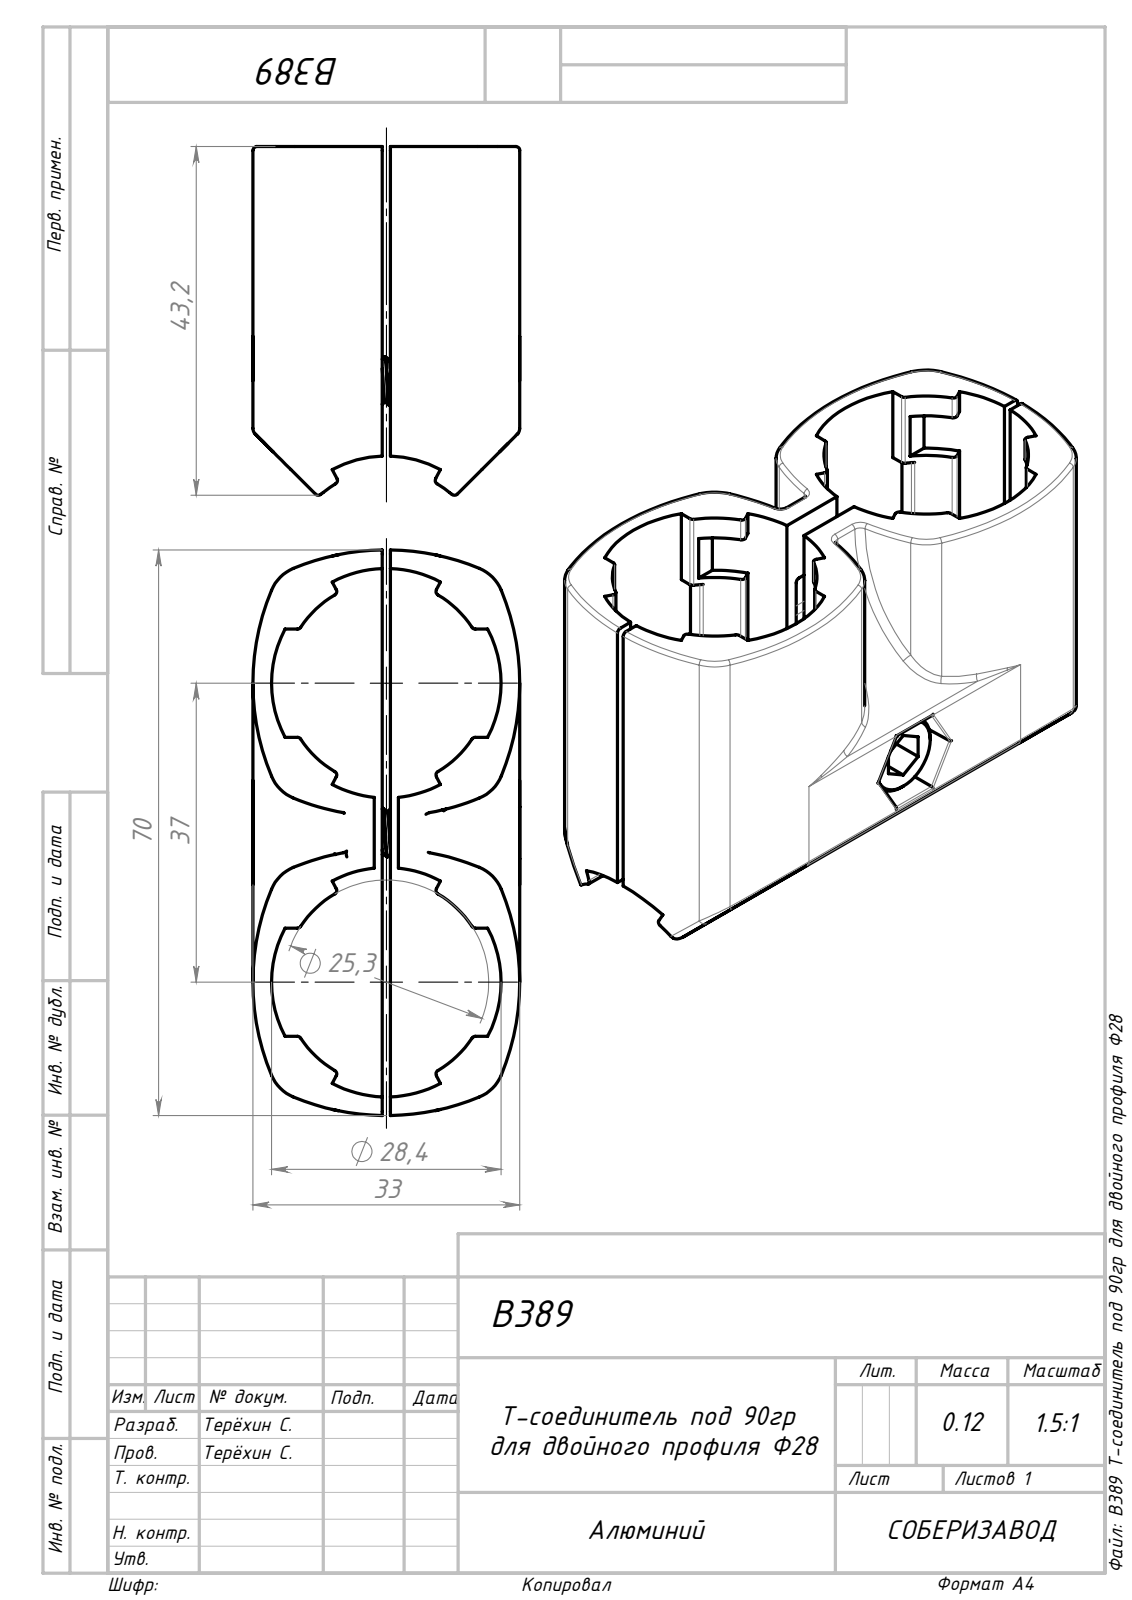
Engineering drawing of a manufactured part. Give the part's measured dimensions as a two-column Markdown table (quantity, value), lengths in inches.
| quantity | value |
| --- | --- |
| part name | B389 Т-соединитель под 90гр для двойного профиля Ф28 |
| STEP written by | SolidWorks 2022 (AUTOMOTIVE_DESIGN) |
| units | inches |
| bodies | 4 solids, 469 faces (150 planar, 198 cylindrical, 121 other) |
| overall size | 2.756 × 1.699 × 1.299 |
| volume | 2.537 in³ |
| surface area | 37.13 in² |
| round holes (diameter × count) | 1.118 × 2, 0.205 × 1, 0.256 × 1 |
| round bosses / shafts (diameter × count) | 0.394 × 1, 0.236 × 1 |
| partial cylindrical surfaces (radius × count) | 0.02 × 62, 0.008 × 12, 0.197 × 9, 1.181 × 8, 0.039 × 4, 0.498 × 2, 1.083 × 2, 1.104 × 2 |
| main face-to-face distances | 0.906, 0.039, 0.394, 0.276, 0.394, 0.669, 0.236, 0.315, 0.63, 0.591 |
| hole center spacings | 1.457 |
